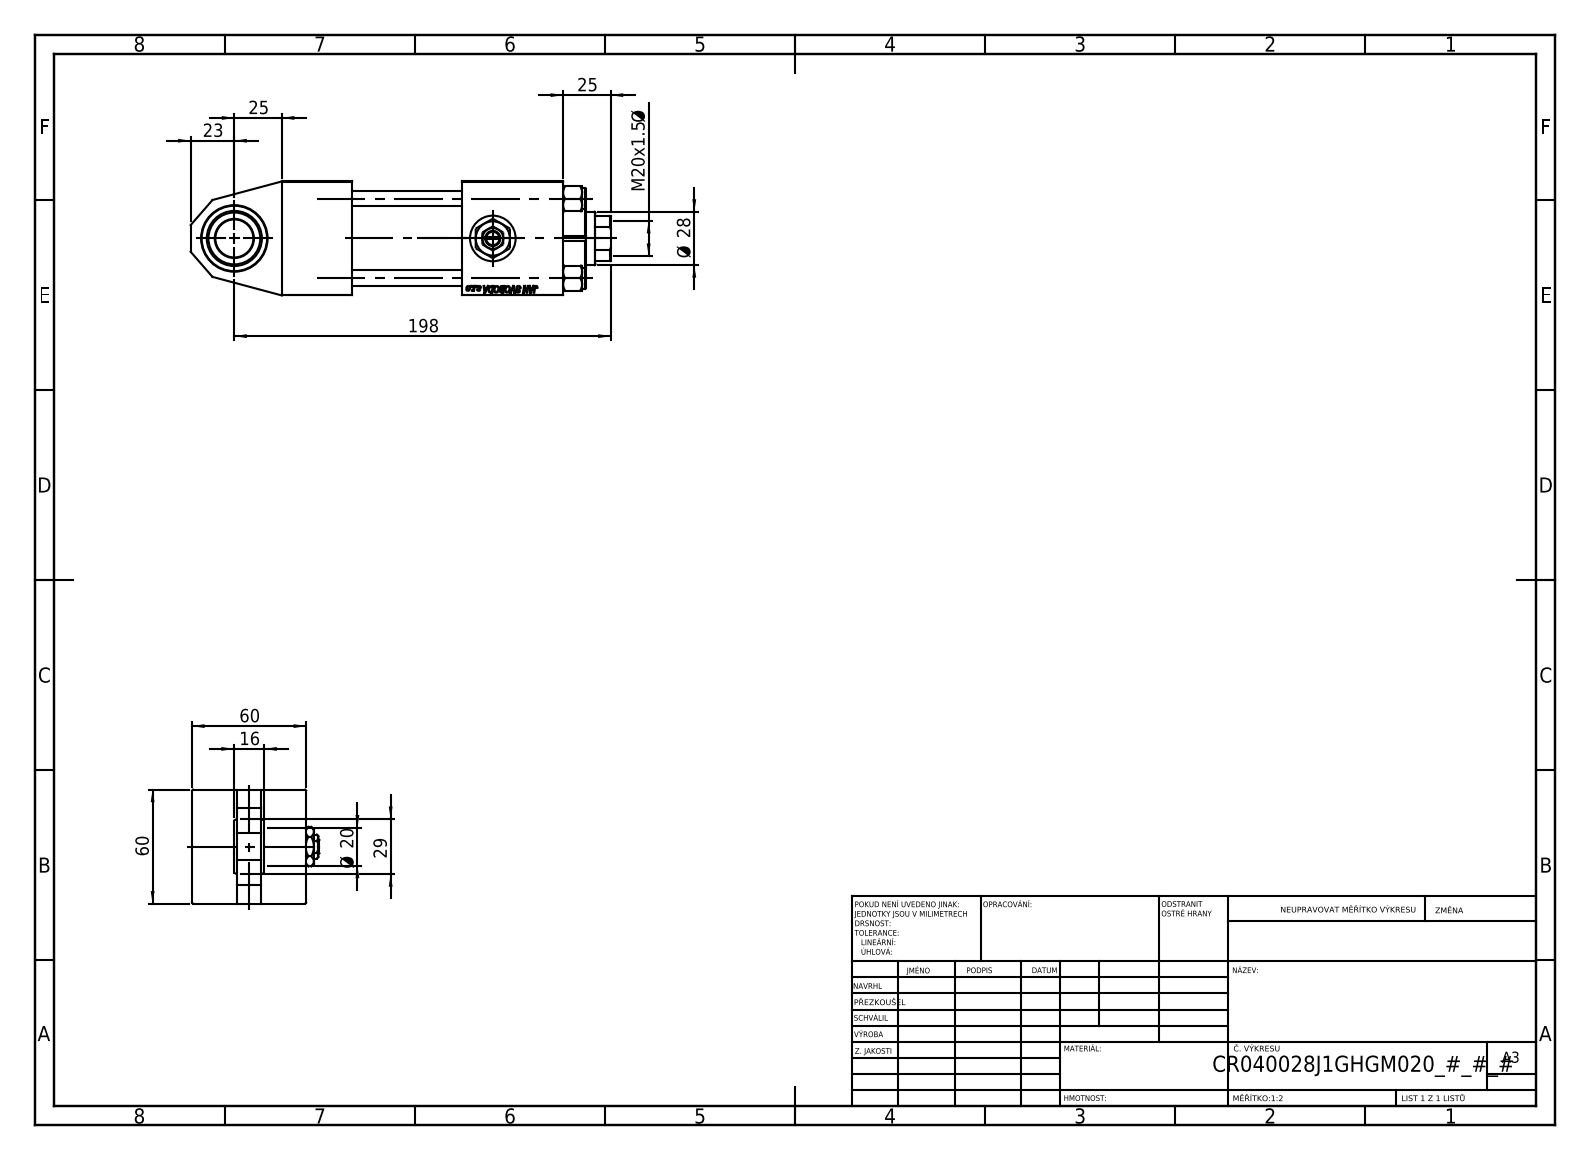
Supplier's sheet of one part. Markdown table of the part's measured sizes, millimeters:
| quantity | value |
| --- | --- |
| part name | Zatka_pro_OIL_PORT; V215_VC_A; V215CR_VCP_J; V215CR_J_Body (+3 more) |
| STEP written by | SolidWorks 2019 (CONFIG_CONTROL_DESIGN) |
| units | millimeters |
| bodies | 13 solids, 1193 faces (540 planar, 93 cylindrical, 560 other) |
| overall size | 221 × 67 × 60 |
| volume | 448 915 mm³ |
| surface area | 122 062 mm² |
| round holes (diameter × count) | 8 × 4, 2.5 × 2, 7 × 2, 16.66 × 2, 24 × 2, 18.5 × 1, 20 × 1, 28 × 1, 31 × 1, 35 × 1, 40 × 1, 45 × 1 |
| round bosses / shafts (diameter × count) | 11 × 4, 46 × 1, 42 × 1 |
| partial cylindrical surfaces (radius × count) | 13.5 × 1 |
| main face-to-face distances | 60, 36.5, 23.5, 37, 53, 58, 95, 148, 111, 13 |
| hole center spacings | 20.85, 29.49, 41.7, 46.53, 20.75, 58.97, 41.5, 43.5 |
